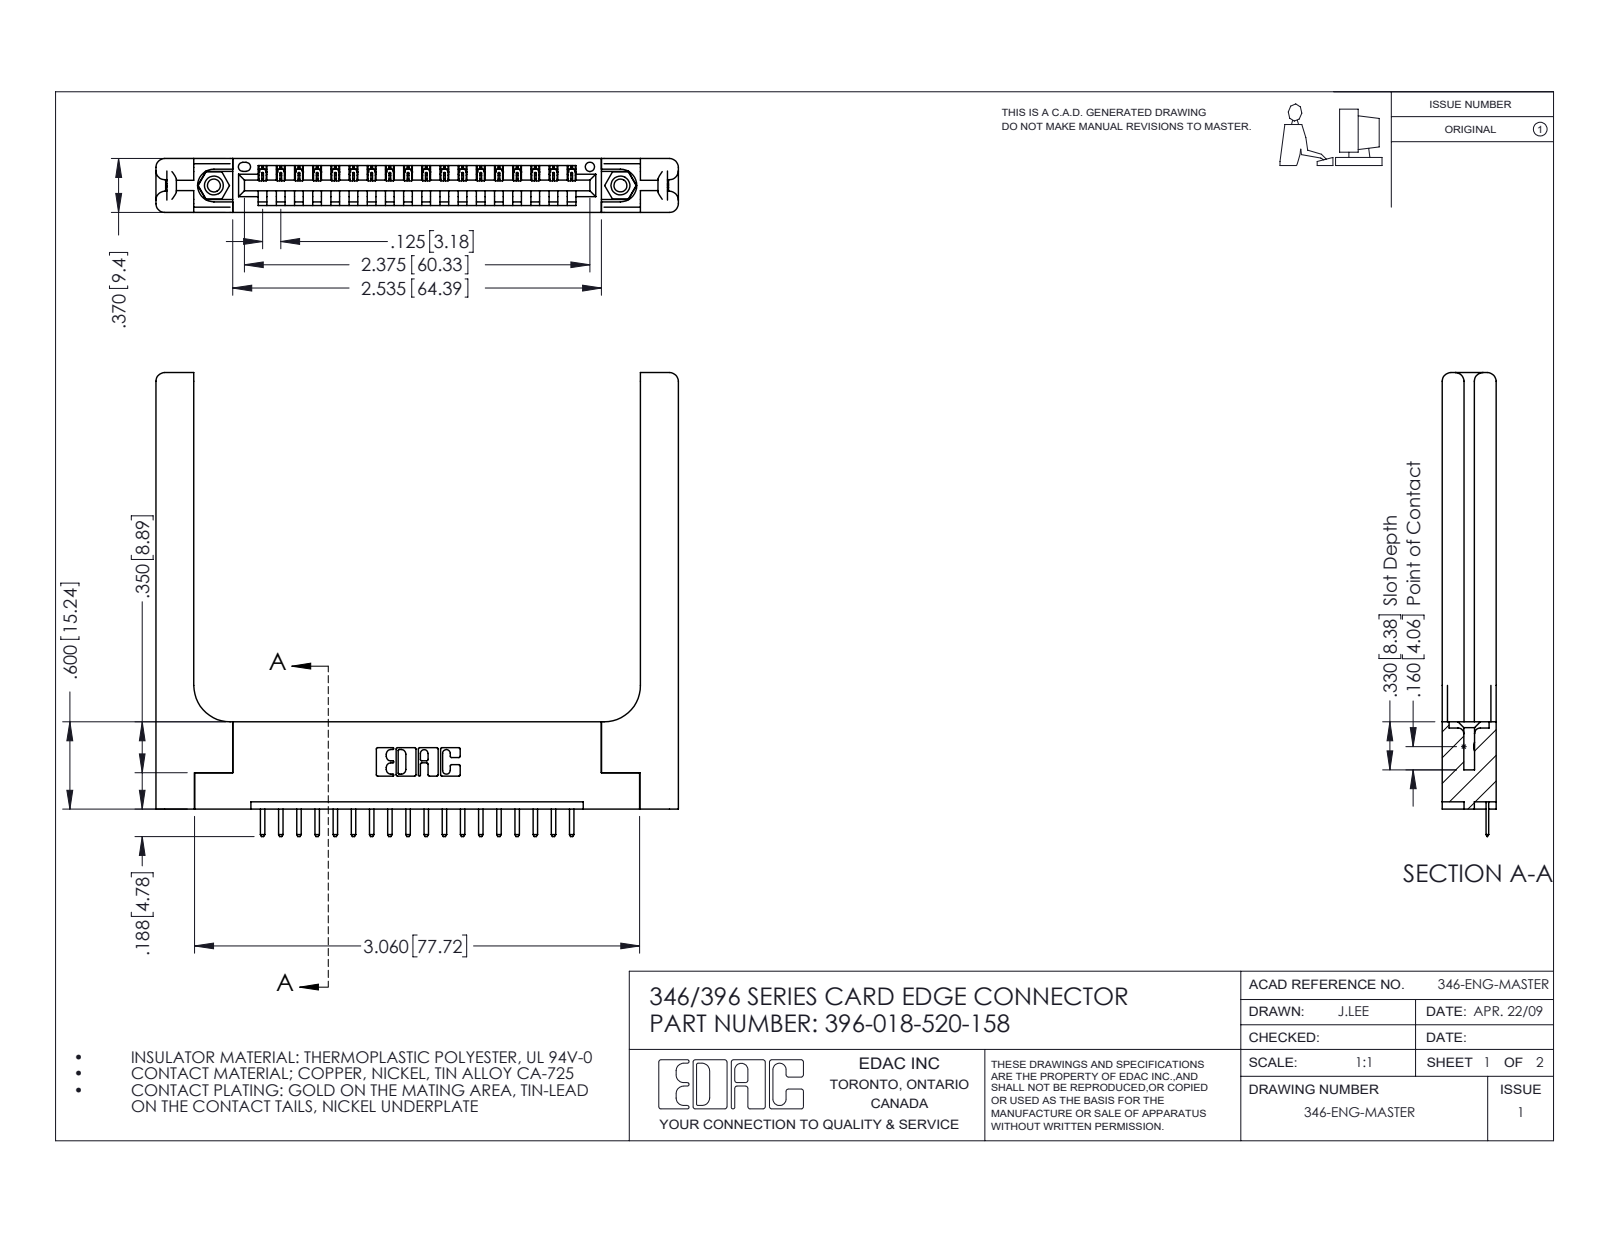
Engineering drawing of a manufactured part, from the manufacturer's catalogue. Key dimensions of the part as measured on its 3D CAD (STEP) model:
Part name (STEP PRODUCT): 346-220-058_345-220-058; 345-250-001_345-250-001-102; 396-018-520-158; 346 Part_Flush Mounting Lugs - 0.156 Dia-TH (+1 more)
STEP written by: SolidWorks 2016 (CONFIG_CONTROL_DESIGN)
Units: inches
Bodies: 23 solids, 1494 faces (980 planar, 454 cylindrical, 60 other)
Overall size (bounding box): 3.591 × 3.188 × 0.37
Volume: 0.978 in³ · Surface area: 23.84 in²
Round holes (diameter × count): ⌀0.089 ×2, ⌀0.125 ×2, ⌀0.156 ×2, ⌀0.064 ×1
Round bosses / shafts (diameter × count): ⌀0.155 ×2
Partial cylindrical surfaces — rounded edges, fillets, slot ends (radius × count): R0.01 ×38, R0.006 ×36, R0.01 ×22, R0.06 ×16, R0.007 ×6, R0.031 ×6, R0.026 ×3, R0.03 ×2
Main face-to-face distances: 0.37, 0.15, 0.072, 0.148, 0.048, 0.322, 0.25, 0.102, 0.22, 0.173
Hole centre spacings: 0.246, 2.588, 2.795
